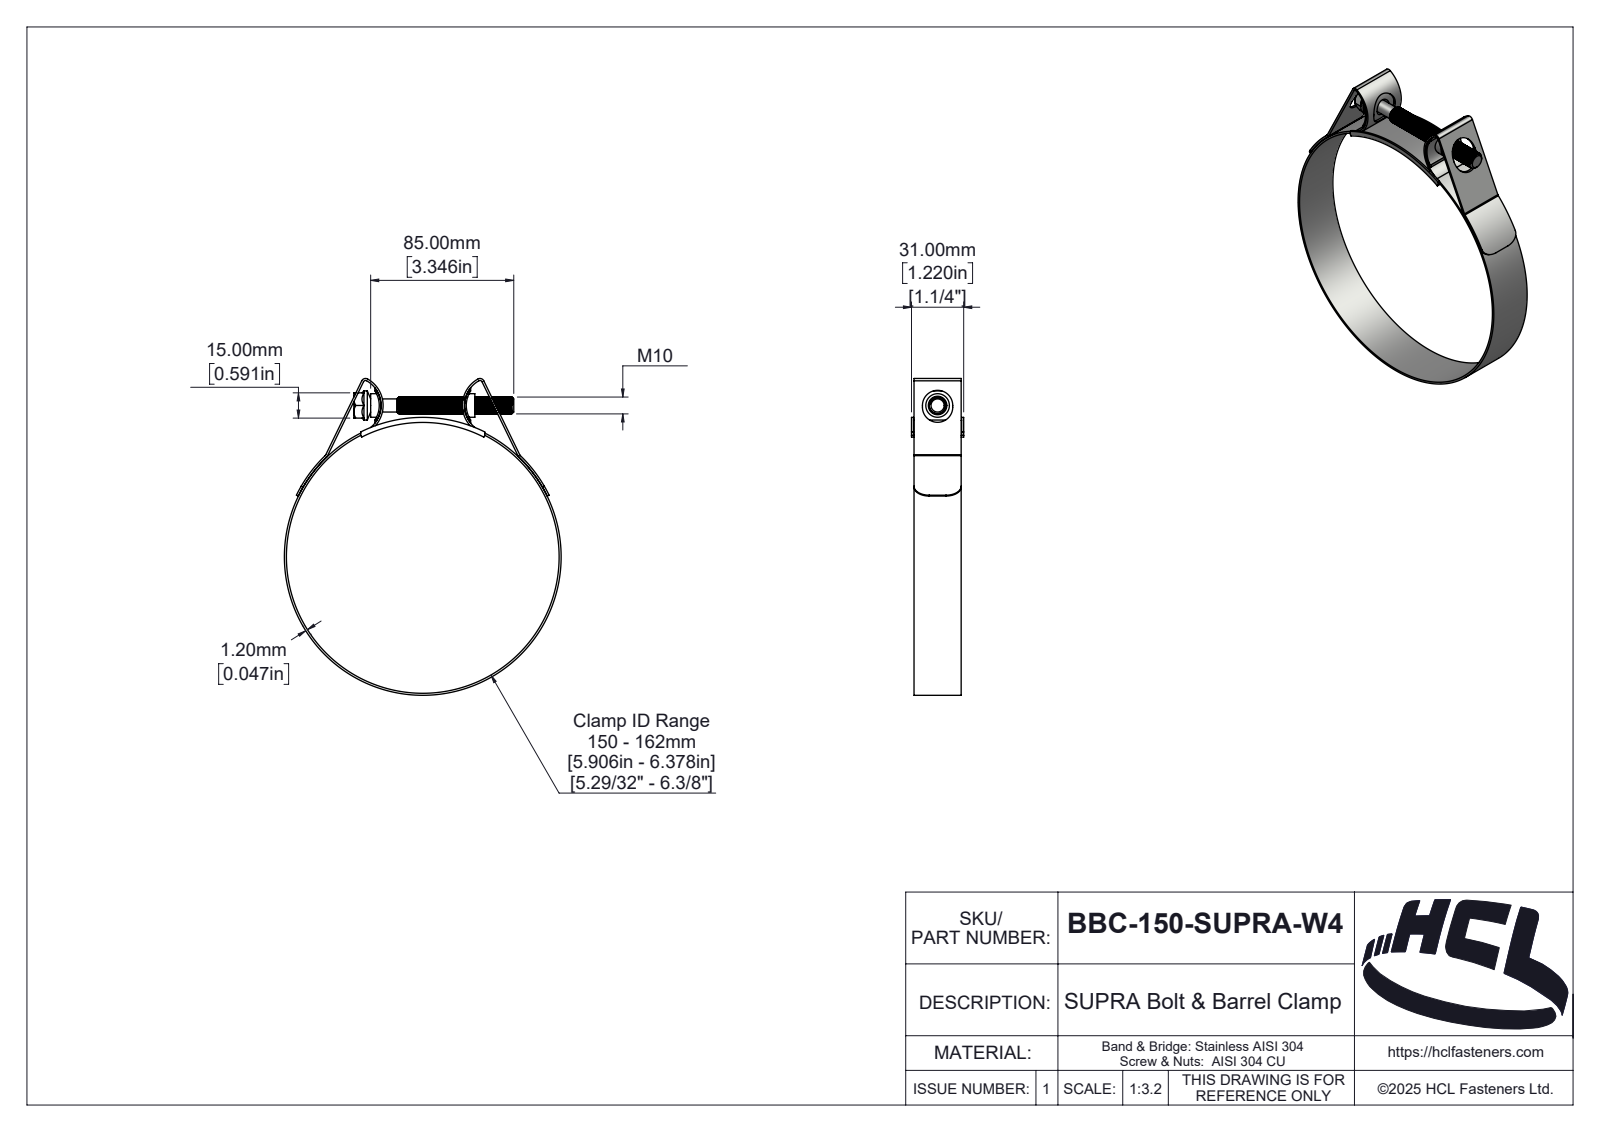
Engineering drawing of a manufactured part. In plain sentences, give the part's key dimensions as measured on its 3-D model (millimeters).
The part is named "BBC-150-SUPRA-W4". Its 3-D file was written by "SolidWorks 2025 (AUTOMOTIVE_DESIGN)". It is 5 solids with 381 faces: 46 planar, 248 cylindrical and 87 other. Overall it measures 188.1 by 164.4 by 31 millimeters. Its volume is 33 786 cubic millimeters and its surface area 50 786 square millimeters. Round holes: 1 of diameter 162. Round bosses or shafts: 1 of diameter 164.4, 1 of diameter 17.32, 1 of diameter 14, 1 of diameter 10, 1 of diameter 7.8. Partial cylindrical surfaces (rounded edges, fillets, slot ends): 4 of radius 1, 2 of radius 1.3, 2 of radius 2, 2 of radius 2.5, 2 of radius 3.2, 2 of radius 9, 2 of radius 15.71, 2 of radius 16.71. The main face-to-face distances are 1.2, 28, 1.5, 29.5, 29.8, 28.3, 31, 28.6, 15, 2.5.
